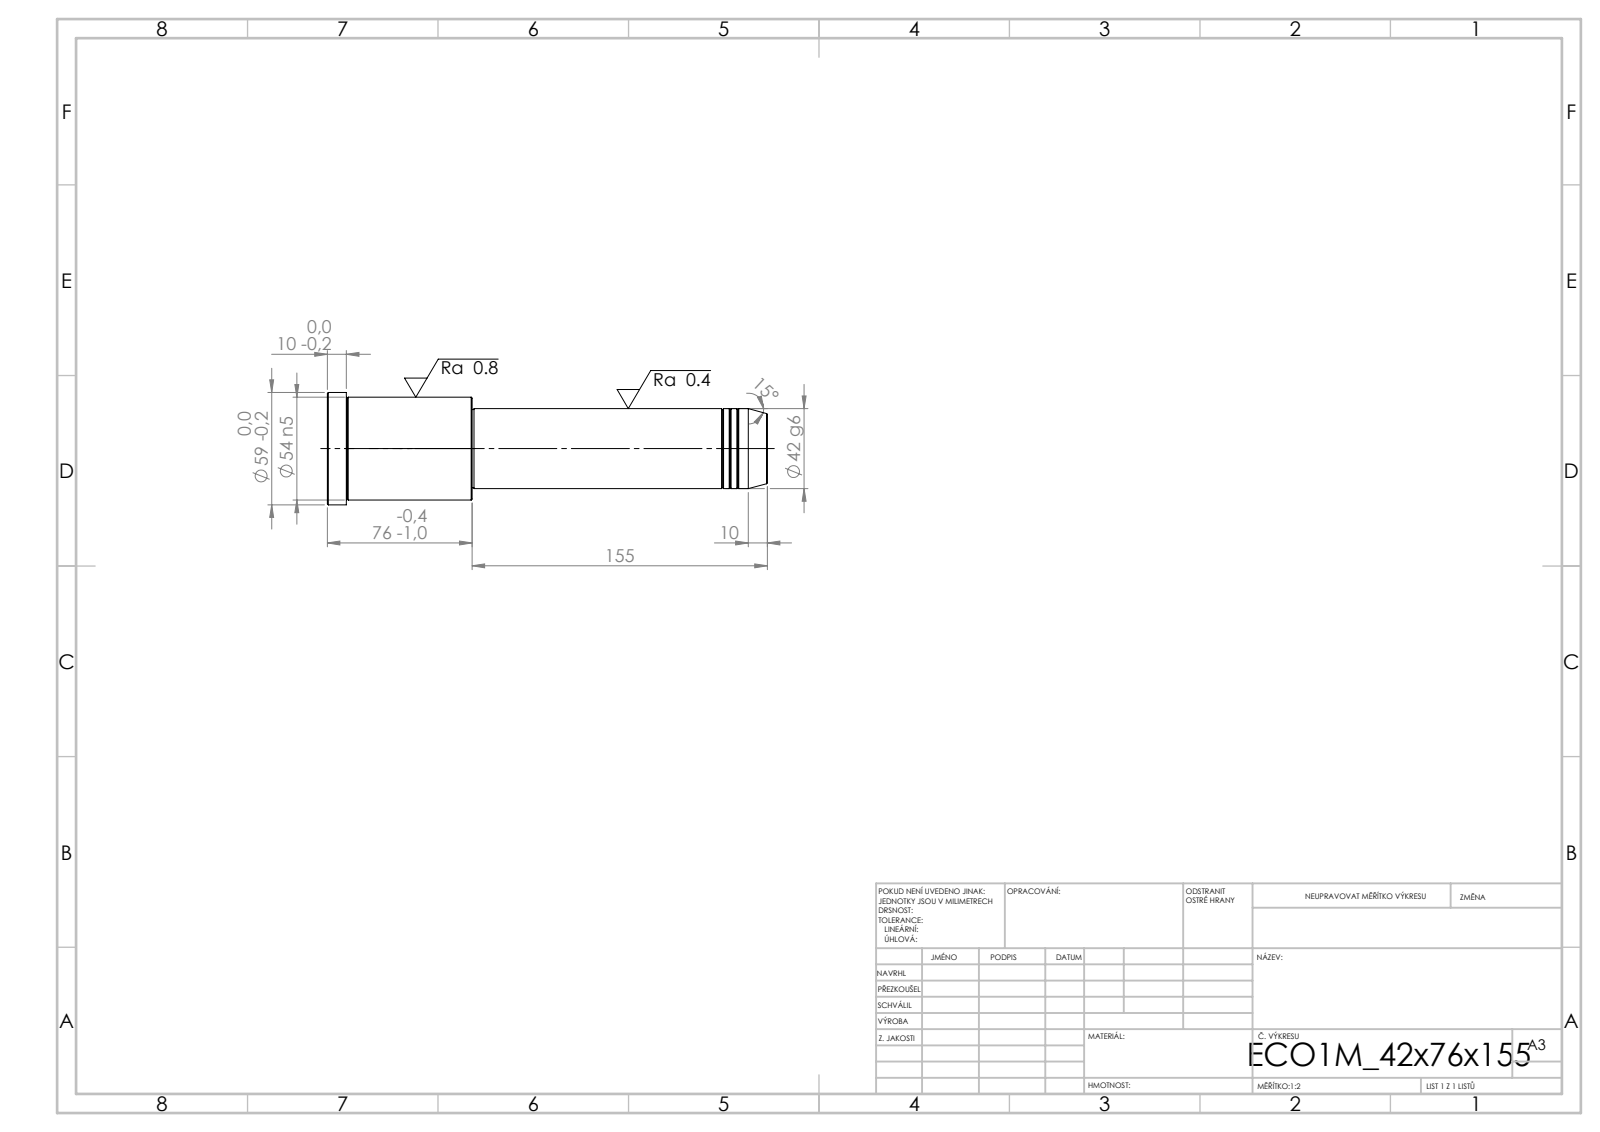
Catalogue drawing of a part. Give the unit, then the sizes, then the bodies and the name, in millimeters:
Units: millimetres
Overall size (bounding box): 231 × 59 × 59
Round bosses / shafts (diameter × count): ⌀59 ×1, ⌀54 ×1, ⌀42 ×1, ⌀41 ×1
Main face-to-face distances: 231, 155, 76, 221, 66, 10, 154, 1, 67, 77
Volume: 391 213 mm³ · Surface area: 38 918 mm²
Bodies: 1 solid, 43 faces (5 planar, 14 cylindrical, 24 other)
STEP written by: SolidWorks 2019 (CONFIG_CONTROL_DESIGN)
